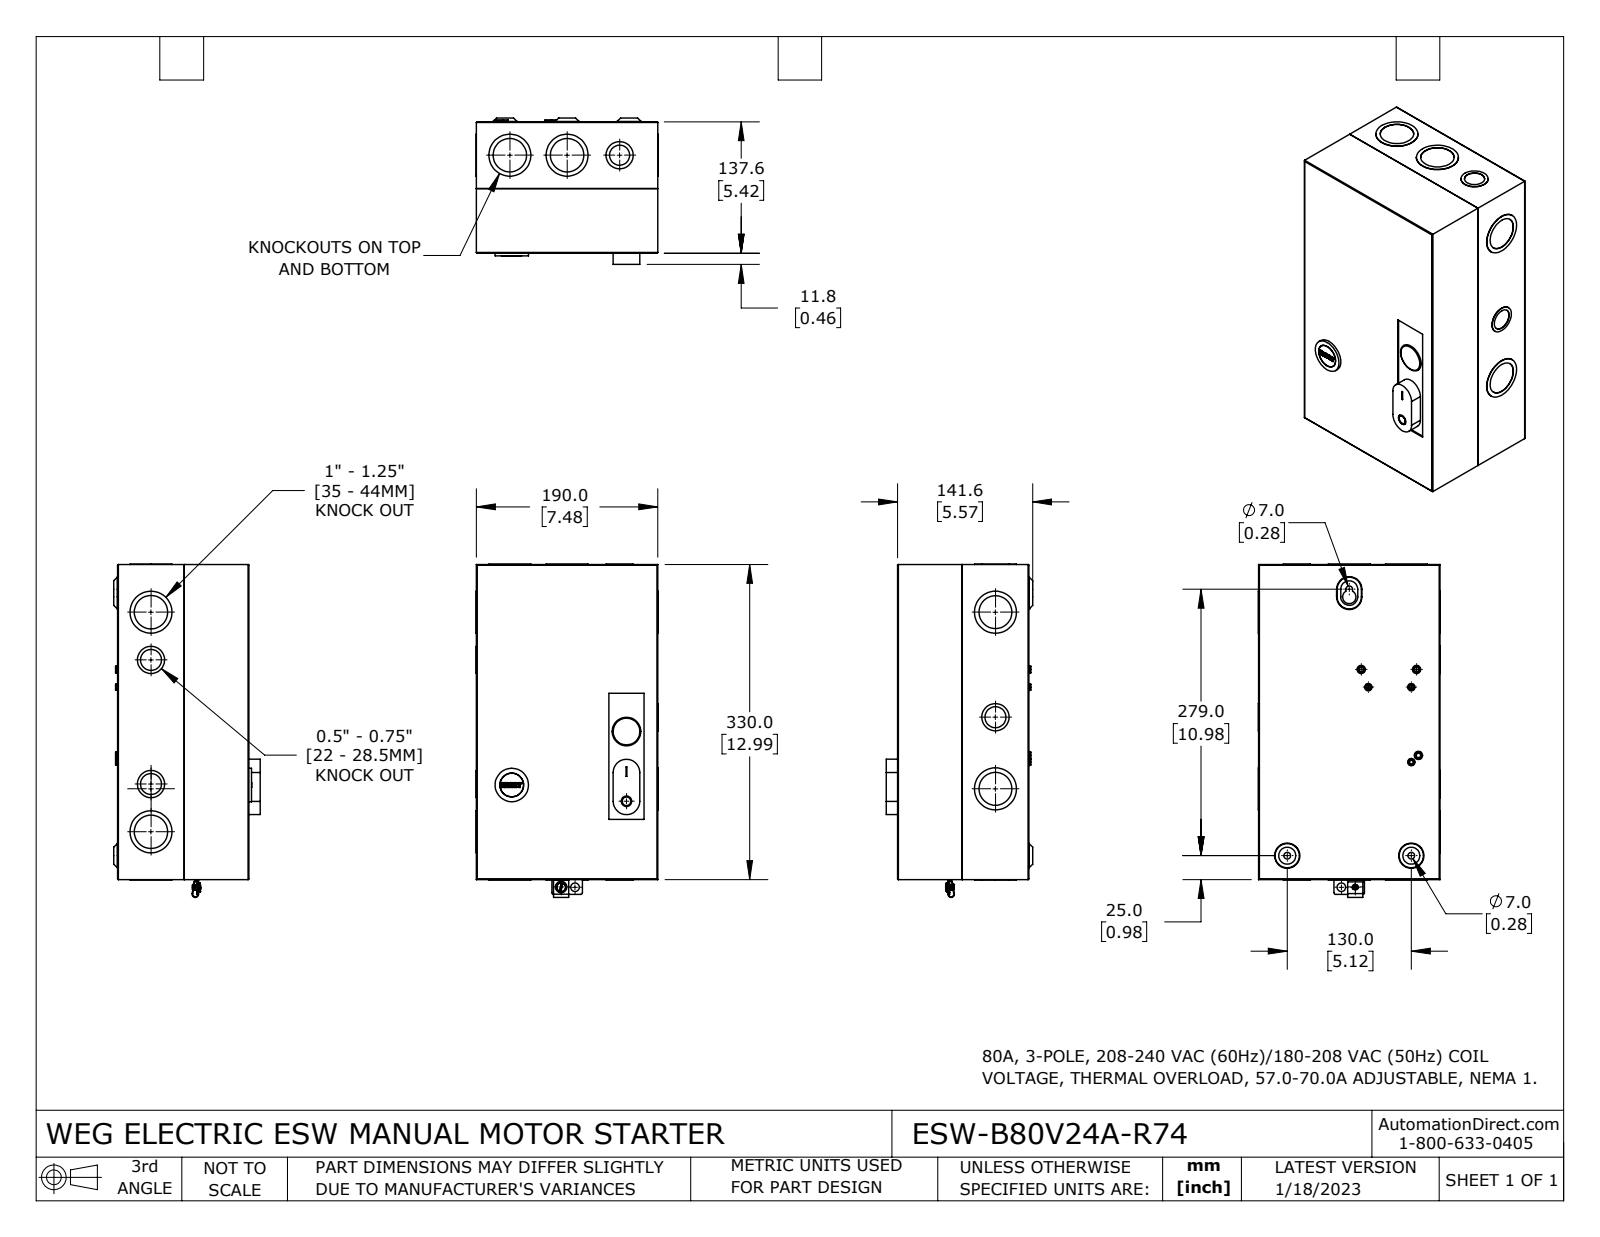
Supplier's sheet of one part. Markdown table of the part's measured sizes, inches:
| quantity | value |
| --- | --- |
| part name | ESW-B80V24A-R74 |
| STEP written by | SolidWorks 2021 (CONFIG_CONTROL_DESIGN) |
| units | inches |
| bodies | 7 solids, 435 faces (161 planar, 221 cylindrical, 53 other) |
| overall size | 13.74 × 7.504 × 6.039 |
| volume | 24.58 in³ |
| surface area | 936.7 in² |
| round holes (diameter × count) | 1.378 × 4, 0.146 × 3, 0.183 × 3, 0.276 × 2, 0.866 × 2, 0.886 × 2, 1.357 × 2, 0.256 × 1, 0.279 × 1, 0.354 × 1, 0.433 × 1, 0.469 × 1 |
| round bosses / shafts (diameter × count) | 1.732 × 4, 1.122 × 3, 0.278 × 3, 0.24 × 3, 1.734 × 2, 1.378 × 1, 1.193 × 1, 1.148 × 1 |
| partial cylindrical surfaces (radius × count) | 0.004 × 34, 0.031 × 8, 0.079 × 3, 0.138 × 3, 0.059 × 2, 0.075 × 2, 0.108 × 2, 0.122 × 2 |
| main face-to-face distances | 0.047, 5.37, 7.433, 5.323, 5.417, 12.945, 7.386, 7.48, 0.071, 12.898 |
| hole center spacings | 0.571, 1.772, 1.969, 2.283, 2.362, 5.118, 7.087, 10.972 |
